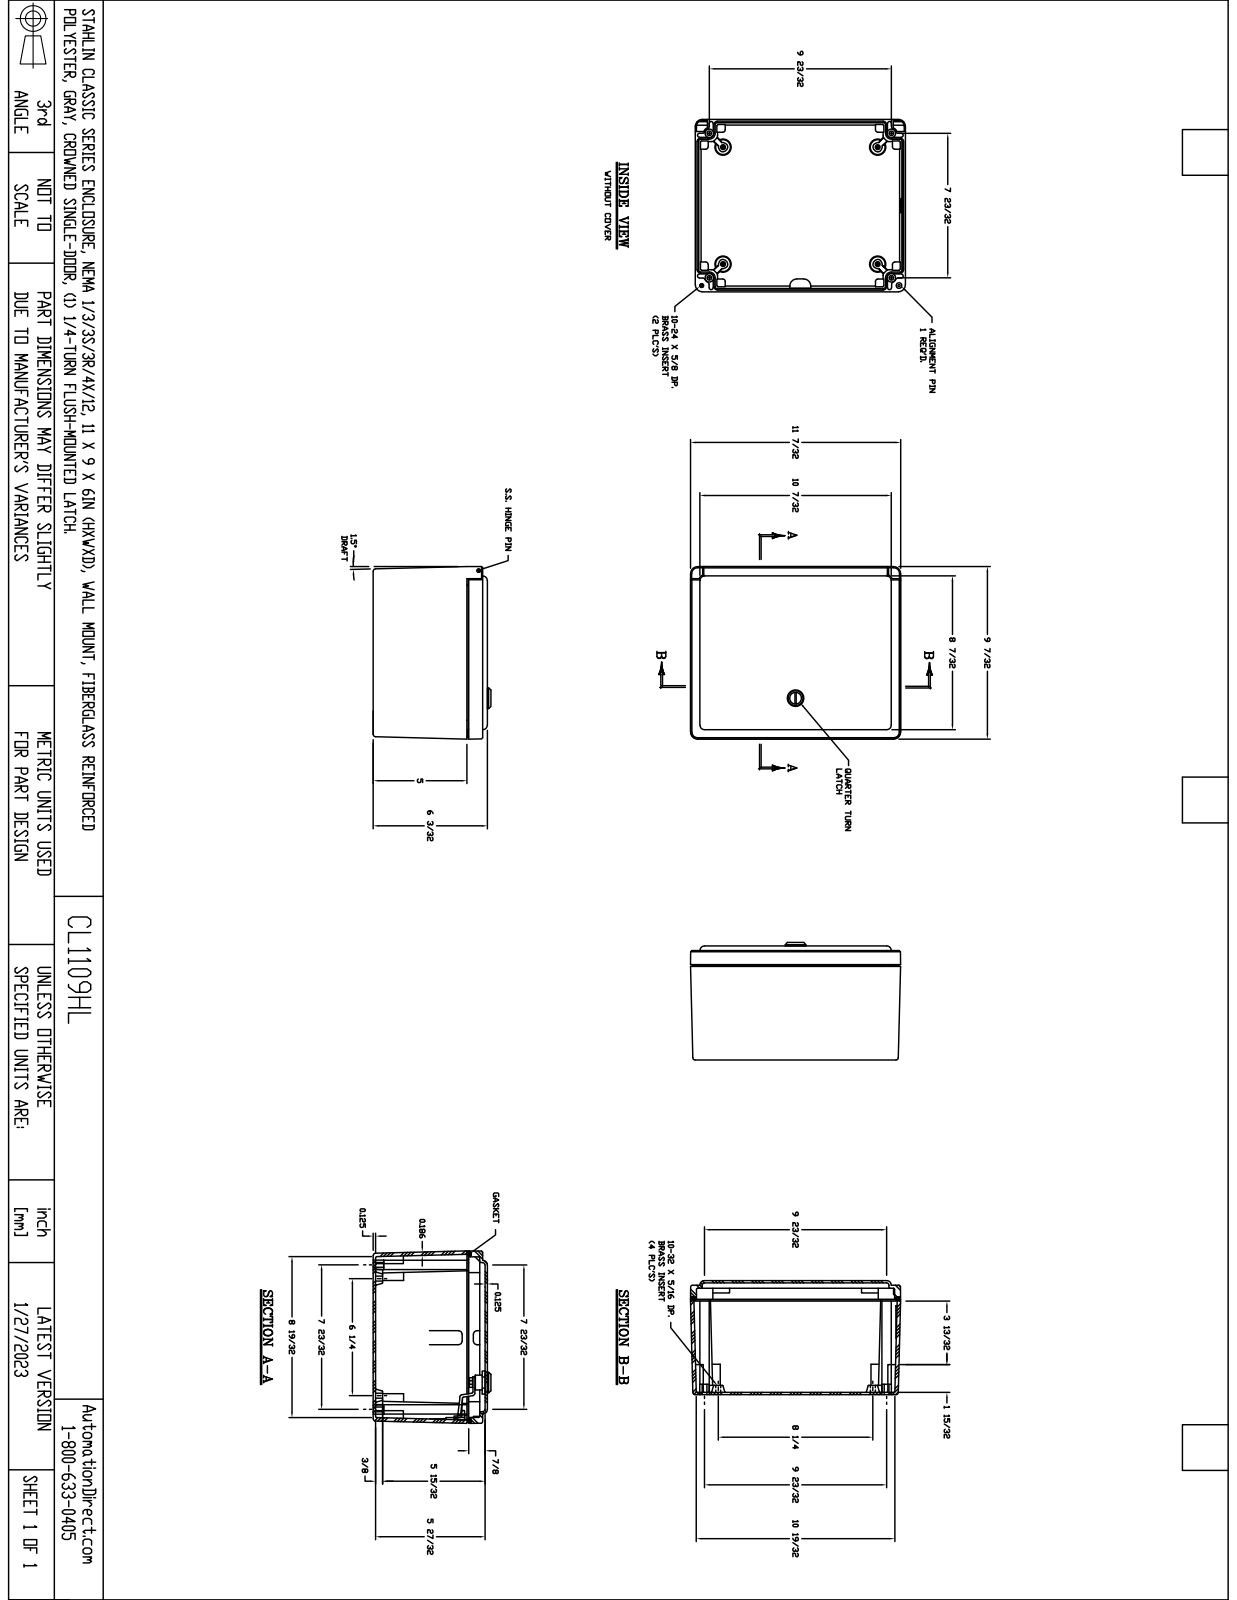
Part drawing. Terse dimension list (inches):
name: CE1109HL
written by: SolidWorks 2018 (AUTOMOTIVE_DESIGN)
unit: in
bodies: 27 solids, 1054 faces (430 planar, 313 cylindrical, 311 other)
size: 11.231 × 9.233 × 6.281
volume: 84.1 in³; area: 980.6 in²
holes: 6× ⌀0.281, 4× ⌀0.156, 4× ⌀0.313, 4× ⌀0.531, 2× ⌀0.096, 2× ⌀0.104, 2× ⌀0.13, 2× ⌀0.14, 2× ⌀0.145, 2× ⌀0.156, 2× ⌀0.179, 2× ⌀0.219
bosses: 2× ⌀0.375, 2× ⌀0.371, 2× ⌀0.234, 2× ⌀0.095, 1× ⌀1.094, 1× ⌀0.63, 1× ⌀0.4, 1× ⌀0.299
rounds: 60× R0.031, 38× R0.125, 16× R0.063, 14× R0.062, 9× R0.313, 8× R0.059, 8× R0.188, 8× R0.25
face distances: 0.125, 5.969, 0.186, 6.094, 5.844, 0.125, 0.25, 5.844, 5.719, 0.75
hole spacings: 1.039, 7.035, 9.026, 11.396, 0.013, 0.528, 0.561, 0.574
